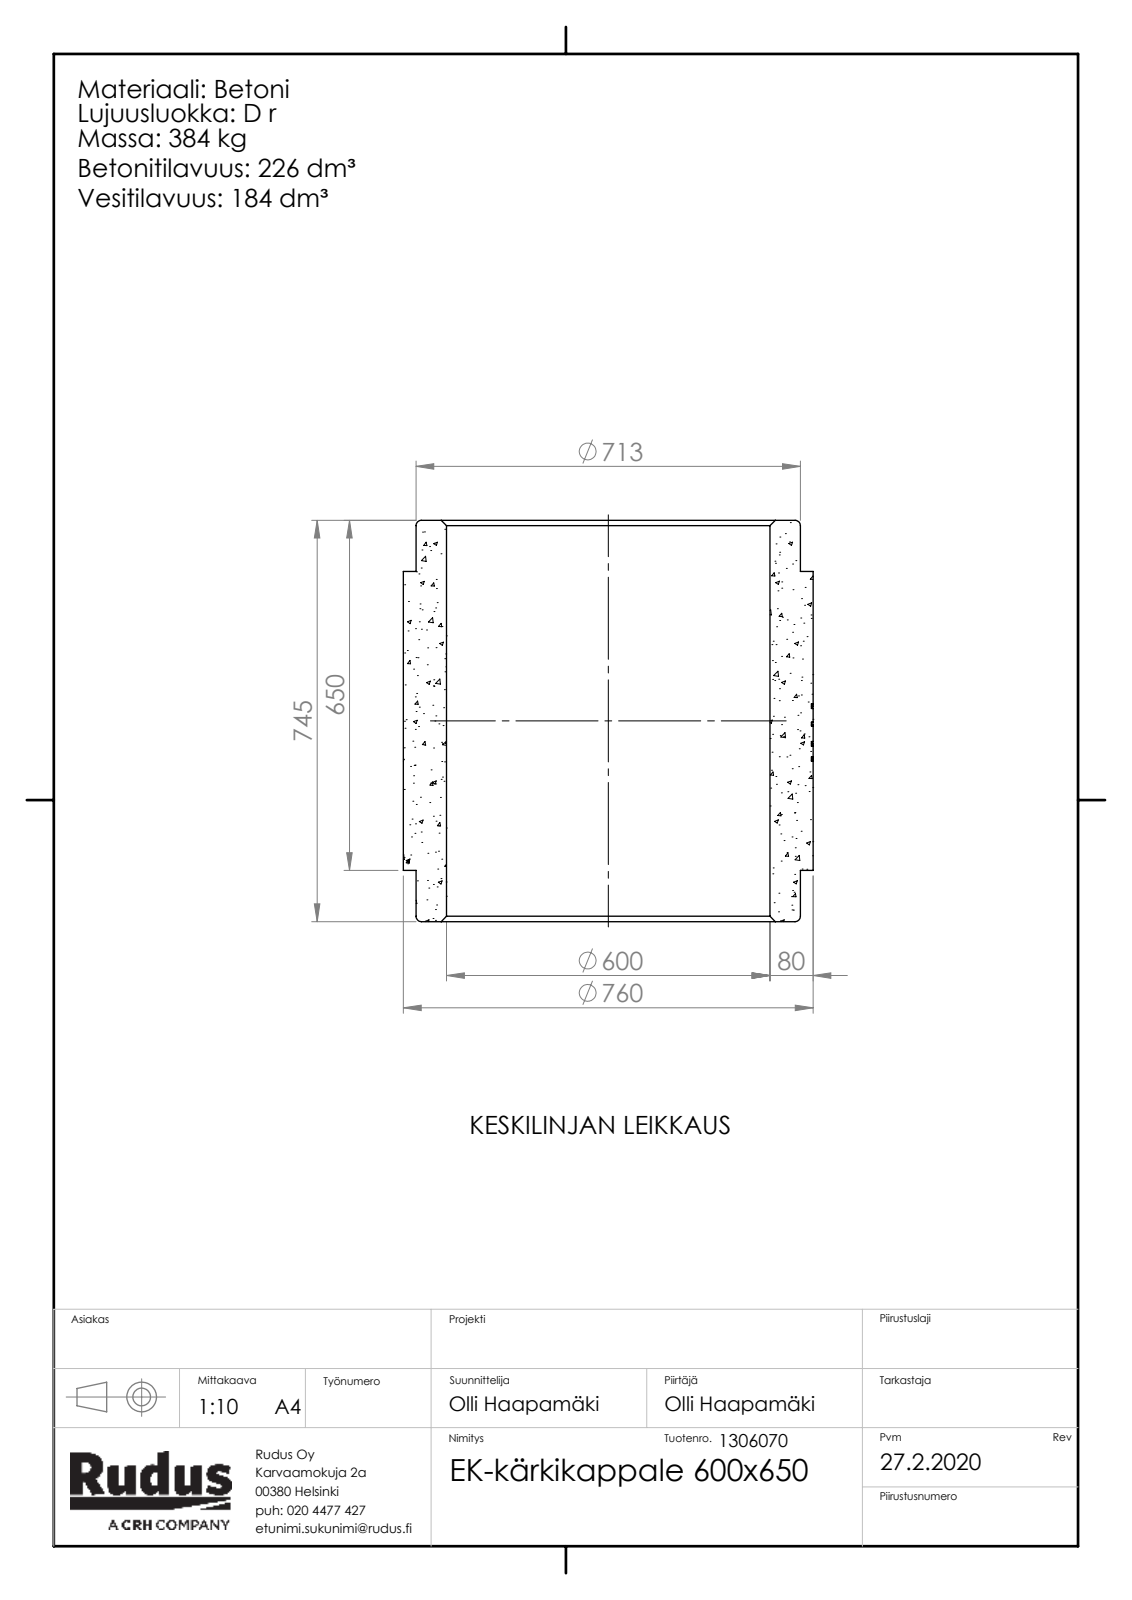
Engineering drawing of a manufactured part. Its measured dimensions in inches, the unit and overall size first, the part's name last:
Units: inches
Overall size (bounding box): 29.921 × 29.921 × 29.331
Round holes (diameter × count): ⌀23.622 ×1
Round bosses / shafts (diameter × count): ⌀29.921 ×1, ⌀28.071 ×1
Partial cylindrical surfaces — rounded edges, fillets, slot ends (radius × count): R14.843 ×1
Main face-to-face distances: 3.74, 25.591, 29.331, 21.85, 15.251, 11.511, 10.34, 14.08, 16.563, 12.823
Volume: 7 121 in³ · Surface area: 5 360 in²
Bodies: 1 solid, 97 faces (8 planar, 15 cylindrical, 74 other)
Part name (STEP PRODUCT): EK-putki-osa-karkikappale; Rudus 1306070 EK-kärkikappale 600x650
STEP written by: SolidWorks 2019 (CONFIG_CONTROL_DESIGN)
